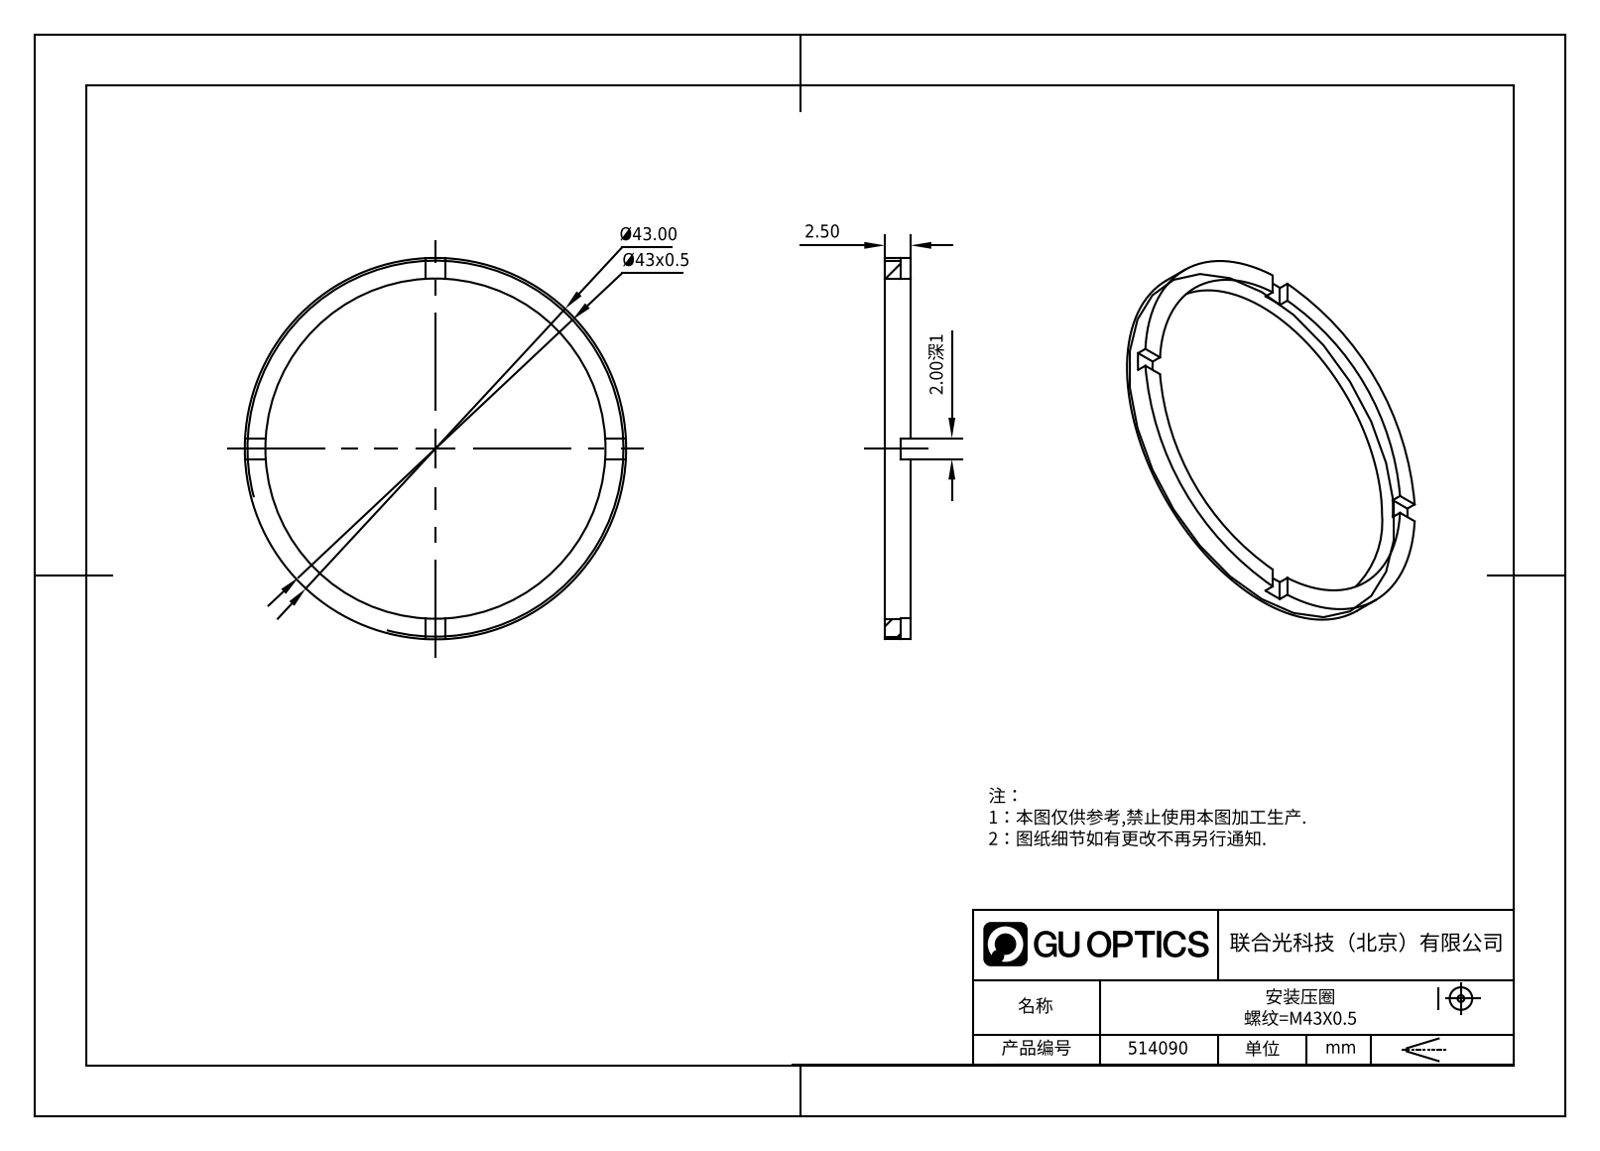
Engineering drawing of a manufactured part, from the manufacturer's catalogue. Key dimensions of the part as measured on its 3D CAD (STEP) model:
Part name (STEP PRODUCT): 514090
STEP written by: SolidWorks 2020 (CONFIG_CONTROL_DESIGN)
Units: millimetres
Bodies: 1 solid, 21 faces (17 planar, 4 cylindrical, 0 other)
Overall size (bounding box): 43 × 43 × 2.5
Volume: 628 mm³ · Surface area: 1 159 mm²
Round holes (diameter × count): ⌀39 ×1
Round bosses / shafts (diameter × count): ⌀43 ×1
Main face-to-face distances: 2.5, 1.5, 1, 2
